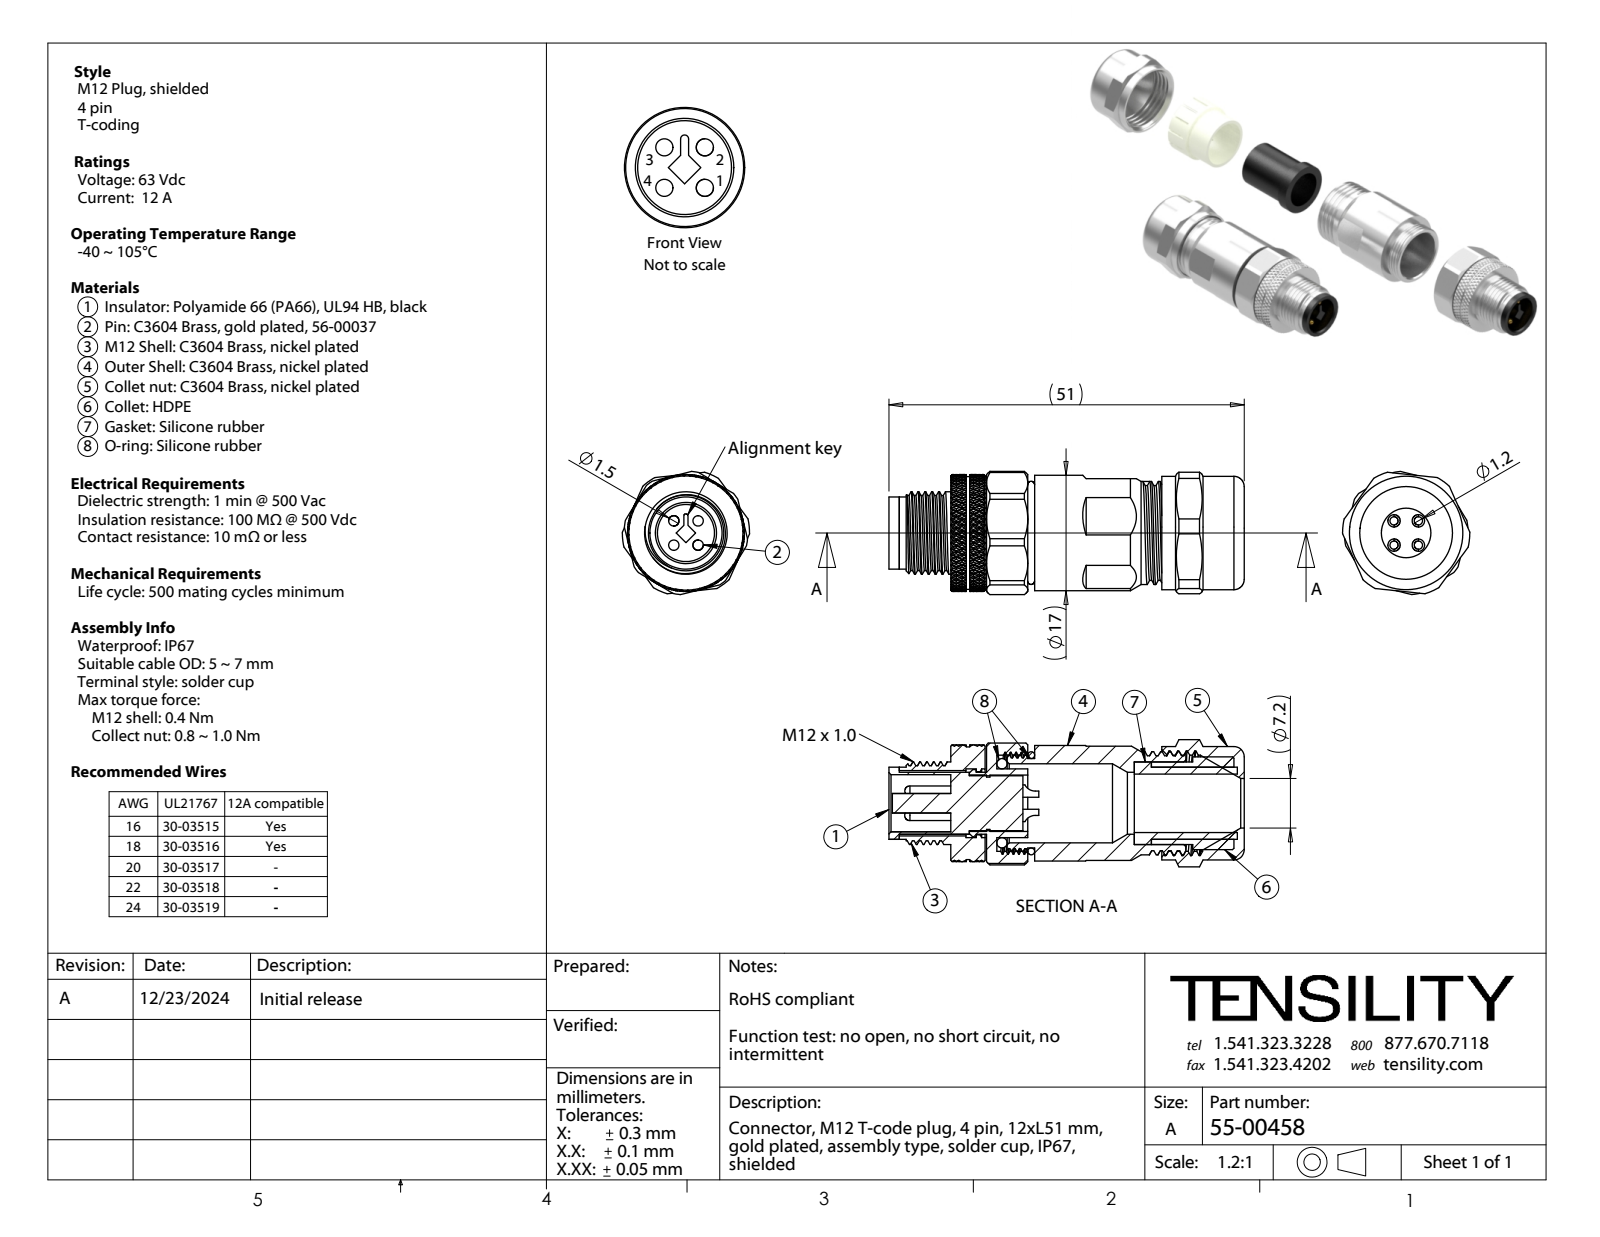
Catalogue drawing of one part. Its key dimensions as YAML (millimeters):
part_name: "55-00458-04; 55-00458; 55-00458-11L; 55-00458-07 (+8 more)"
step_written_by: "SolidWorks 2021 (CONFIG_CONTROL_DESIGN)"
units: millimeters
bodies: {solids: 13, faces: 509, planar: 167, cylindrical: 200, other: 142}
overall_size: [51.7, 18.5, 17.92]
volume: 7044
surface_area: 11173
round_holes:
  - {diameter: 1.2, count: 4}
  - {diameter: 1.5, count: 4}
  - {diameter: 7.2, count: 1}
  - {diameter: 7.6, count: 1}
  - {diameter: 8.2, count: 1}
  - {diameter: 8.3, count: 1}
  - {diameter: 8.5, count: 1}
  - {diameter: 9.2, count: 1}
  - {diameter: 9.5, count: 1}
  - {diameter: 10, count: 1}
  - {diameter: 11.5, count: 1}
  - {diameter: 14, count: 1}
round_bosses_or_shafts:
  - {diameter: 1.8, count: 4}
  - {diameter: 17, count: 1}
  - {diameter: 16.8, count: 1}
  - {diameter: 16.5, count: 1}
  - {diameter: 16.4, count: 1}
  - {diameter: 15, count: 1}
  - {diameter: 13.5, count: 1}
  - {diameter: 13, count: 1}
partial_cylinders:
  - {radius: 1.7, count: 2}
  - {radius: 0.3, count: 1}
  - {radius: 9, count: 1}
  - {radius: 9.25, count: 1}
face_to_face_distances: [17, 1.5, 1, 5, 6, 7.5, 5.2, 30.5, 31.5, 5.5]
hole_center_spacings: [2.5, 3.54, 5.01]
